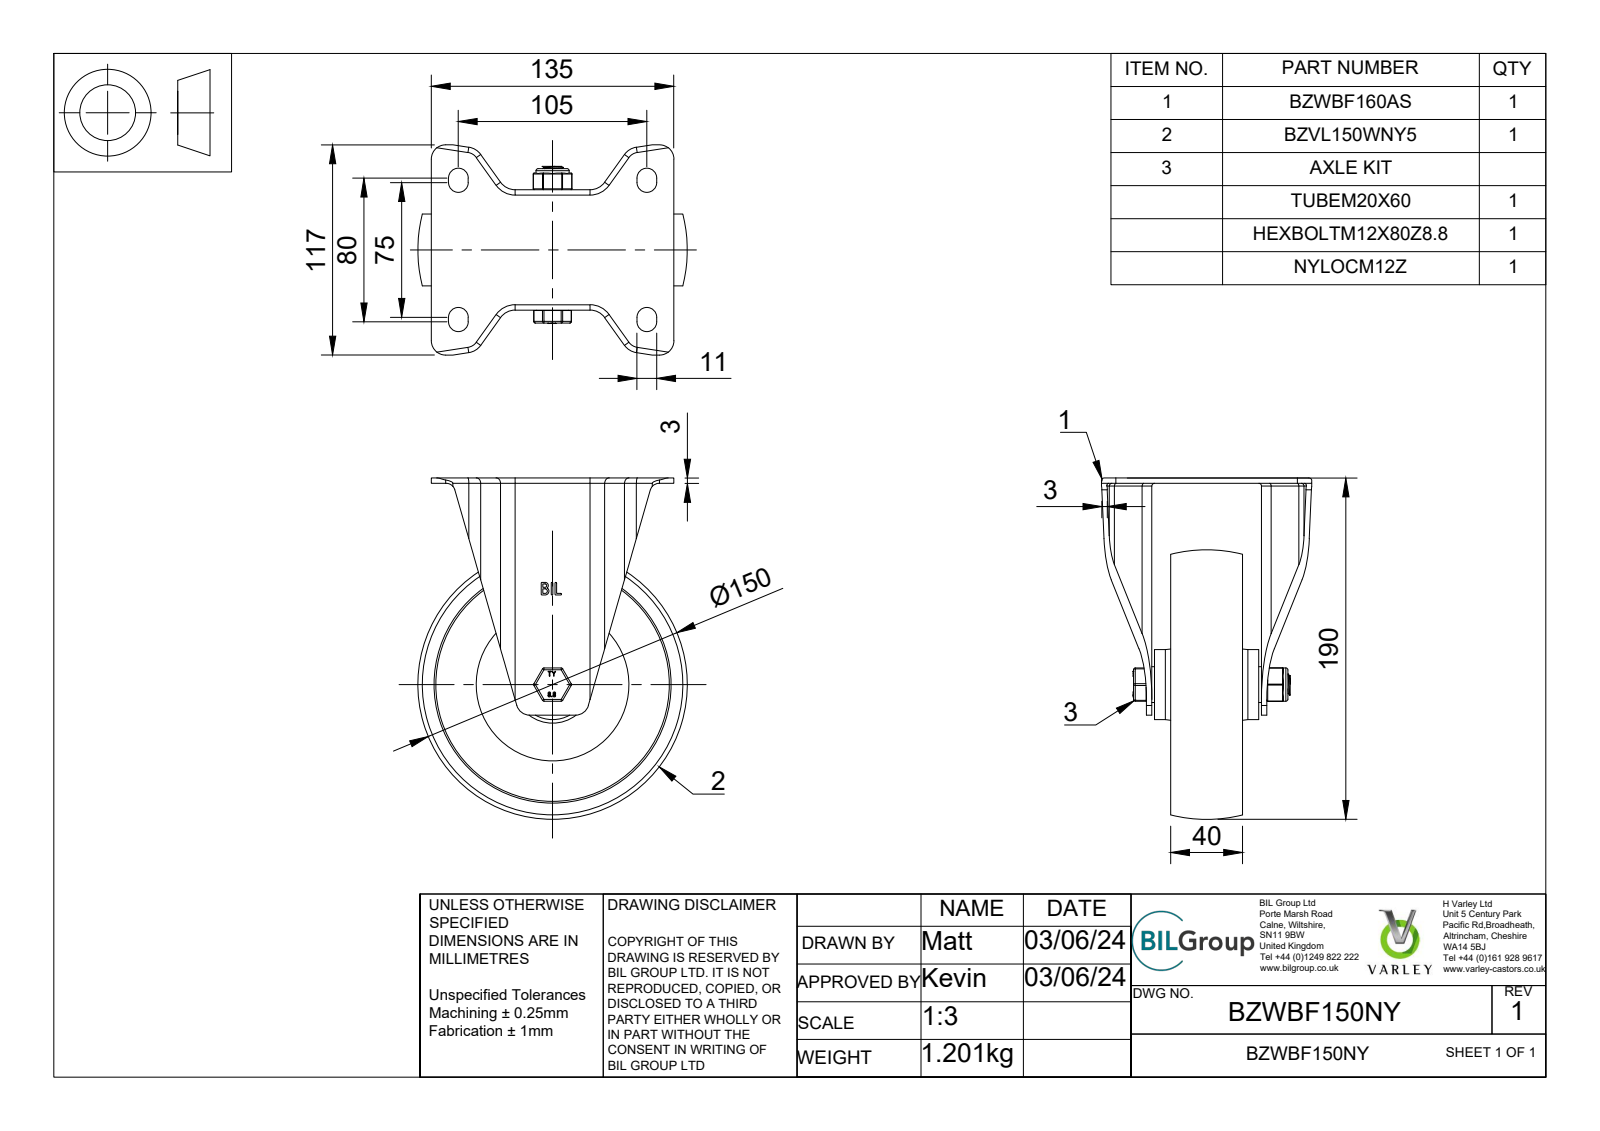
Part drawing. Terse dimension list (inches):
name: BZWBF150NY v3; BZWBF160AS v1; BZWBF160AS; ZINC PLATED, PRESSED STEEL BRACKET (+8 more)
written by: Autodesk Translation Framework v13.14.0.145 (AUTOMOTIVE_DESIGN)
unit: in
bodies: 6 solids, 366 faces (134 planar, 140 cylindrical, 92 other)
size: 7.48 × 5.906 × 4.606
volume: 24.83 in³; area: 244.2 in²
holes: 1× ⌀0.472, 1× ⌀0.48, 1× ⌀0.492, 1× ⌀0.551, 1× ⌀0.807
bosses: 1× ⌀1.535, 1× ⌀0.783, 1× ⌀0.728, 1× ⌀0.709, 1× ⌀0.466, 1× ⌀0.387
rounds: 18× R0.02, 12× R0.039, 10× R0.059, 10× R0.118, 8× R0.217, 8× R0.394, 4× R0.276, 4× R0.315
face distances: 0.118, 1.102, 1.299, 1.22, 1.417, 2.52, 0.197, 0.689, 0.413, 0.531
